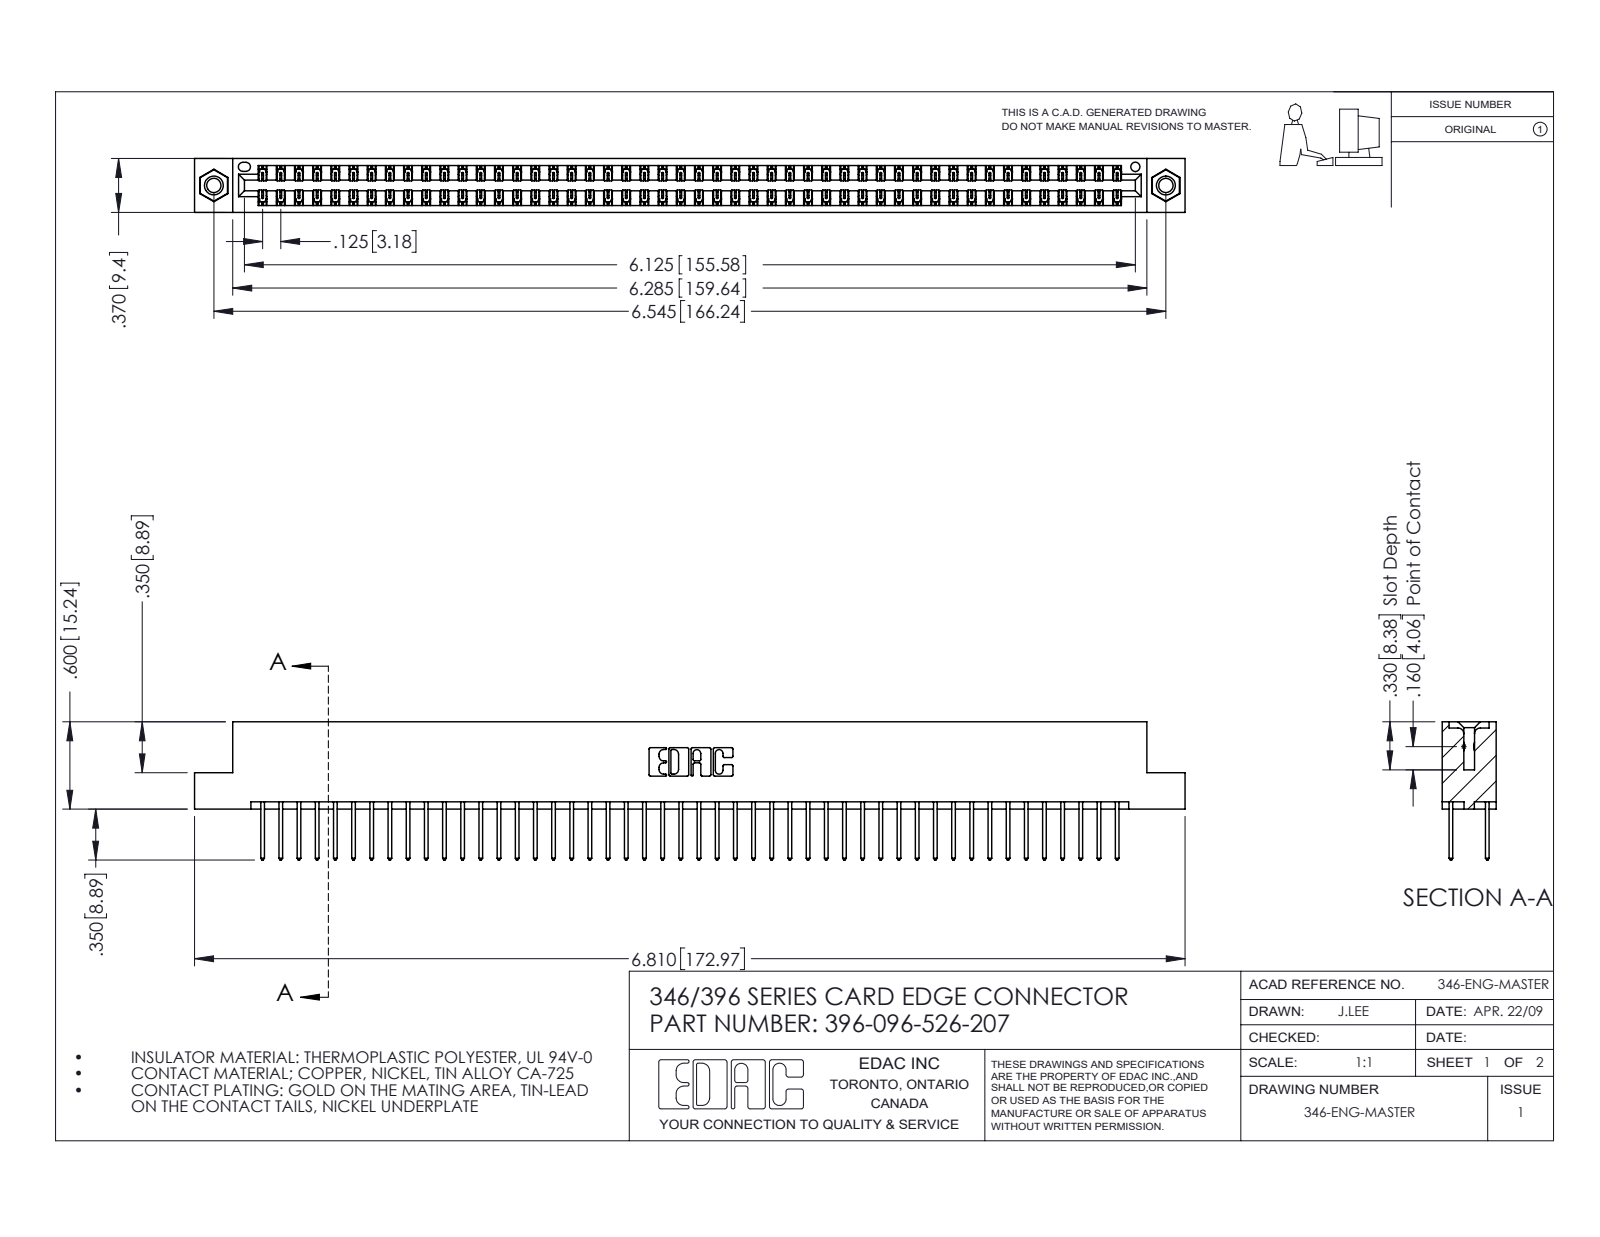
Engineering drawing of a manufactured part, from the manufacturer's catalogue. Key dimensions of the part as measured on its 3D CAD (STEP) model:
Part name (STEP PRODUCT): 396-096-526-207; 345-250-001_345-250-005-103; 345-292-001_345-293-126; 346 Part_Flush Mounting Lugs - 0.156 Dia-TI
STEP written by: SolidWorks 2016 (CONFIG_CONTROL_DESIGN)
Units: inches
Bodies: 99 solids, 5174 faces (3468 planar, 1690 cylindrical, 16 other)
Overall size (bounding box): 6.81 × 0.95 × 0.37
Volume: 1.041 in³ · Surface area: 37.63 in²
Round holes (diameter × count): ⌀0.098 ×2, ⌀0.125 ×2, ⌀0.156 ×2, ⌀0.064 ×1
Round bosses / shafts (diameter × count): ⌀0.155 ×2
Partial cylindrical surfaces — rounded edges, fillets, slot ends (radius × count): R0.006 ×144, R0.01 ×96, R0.01 ×22, R0.007 ×6, R0.031 ×6, R0.026 ×3, R0.014 ×2, R0.022 ×2
Main face-to-face distances: 0.048, 0.322, 0.25, 0.37, 0.072, 0.298, 0.025, 0.275, 0.148, 0.222
Hole centre spacings: 0.246, 6.336, 6.545
